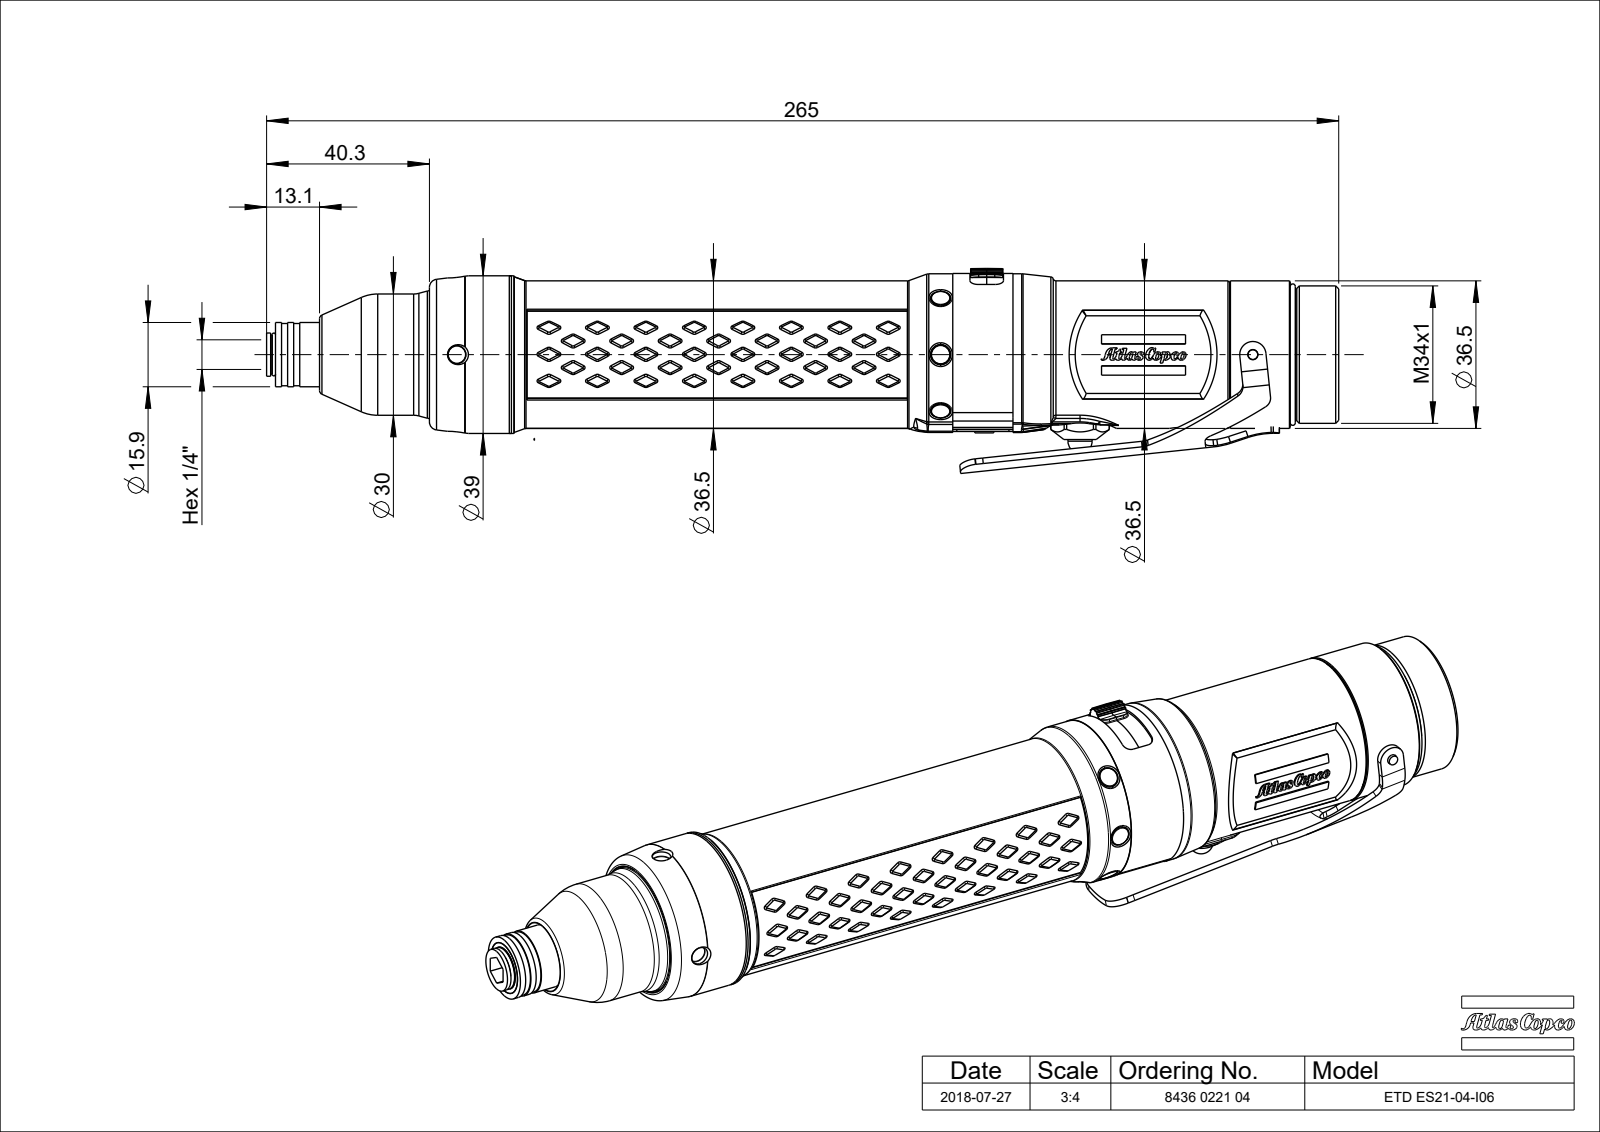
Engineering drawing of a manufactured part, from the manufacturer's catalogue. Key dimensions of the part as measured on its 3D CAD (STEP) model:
Part name (STEP PRODUCT): 4220394770_AF2; 4220394712_TPE_AF1; 4220394772_AF1_ASM; 4220394701_AF1 (+8 more)
STEP written by: CREO PARAMETRIC BY PTC INC, 2016260 (CONFIG_CONTROL_DESIGN)
Units: millimetres
Bodies: 30 solids, 4308 faces (1214 planar, 863 cylindrical, 2231 other)
Overall size (bounding box): 265.35 × 50.73 × 42.25
Volume: 109 645 mm³ · Surface area: 124 331 mm²
Round holes (diameter × count): ⌀2.64 ×12, ⌀3.27 ×12, ⌀3.6 ×12, ⌀5 ×10, ⌀4.2 ×5, ⌀0.6 ×4, ⌀0.8 ×4, ⌀1.7 ×4, ⌀2.7 ×2, ⌀4.5 ×2, ⌀6 ×2, ⌀9 ×2
Round bosses / shafts (diameter × count): ⌀2.55 ×6, ⌀1.6 ×6, ⌀3.06 ×4, ⌀2.63 ×4, ⌀2.45 ×4, ⌀2.25 ×4, ⌀1.56 ×4, ⌀3.1 ×2
Partial cylindrical surfaces — rounded edges, fillets, slot ends (radius × count): R0.2 ×48, R0.1 ×34, R1 ×27, R2.25 ×16, R1.6 ×12, R5 ×12, R0.3 ×10, R3 ×10
Main face-to-face distances: 0.5, 162.92, 61.88, 0.51, 6.34, 14.89, 148.03, 61.53, 76.42, 224.45
Hole centre spacings: 5.88, 9.51, 5.19, 13.44, 16.94, 18.08, 18.77, 3
